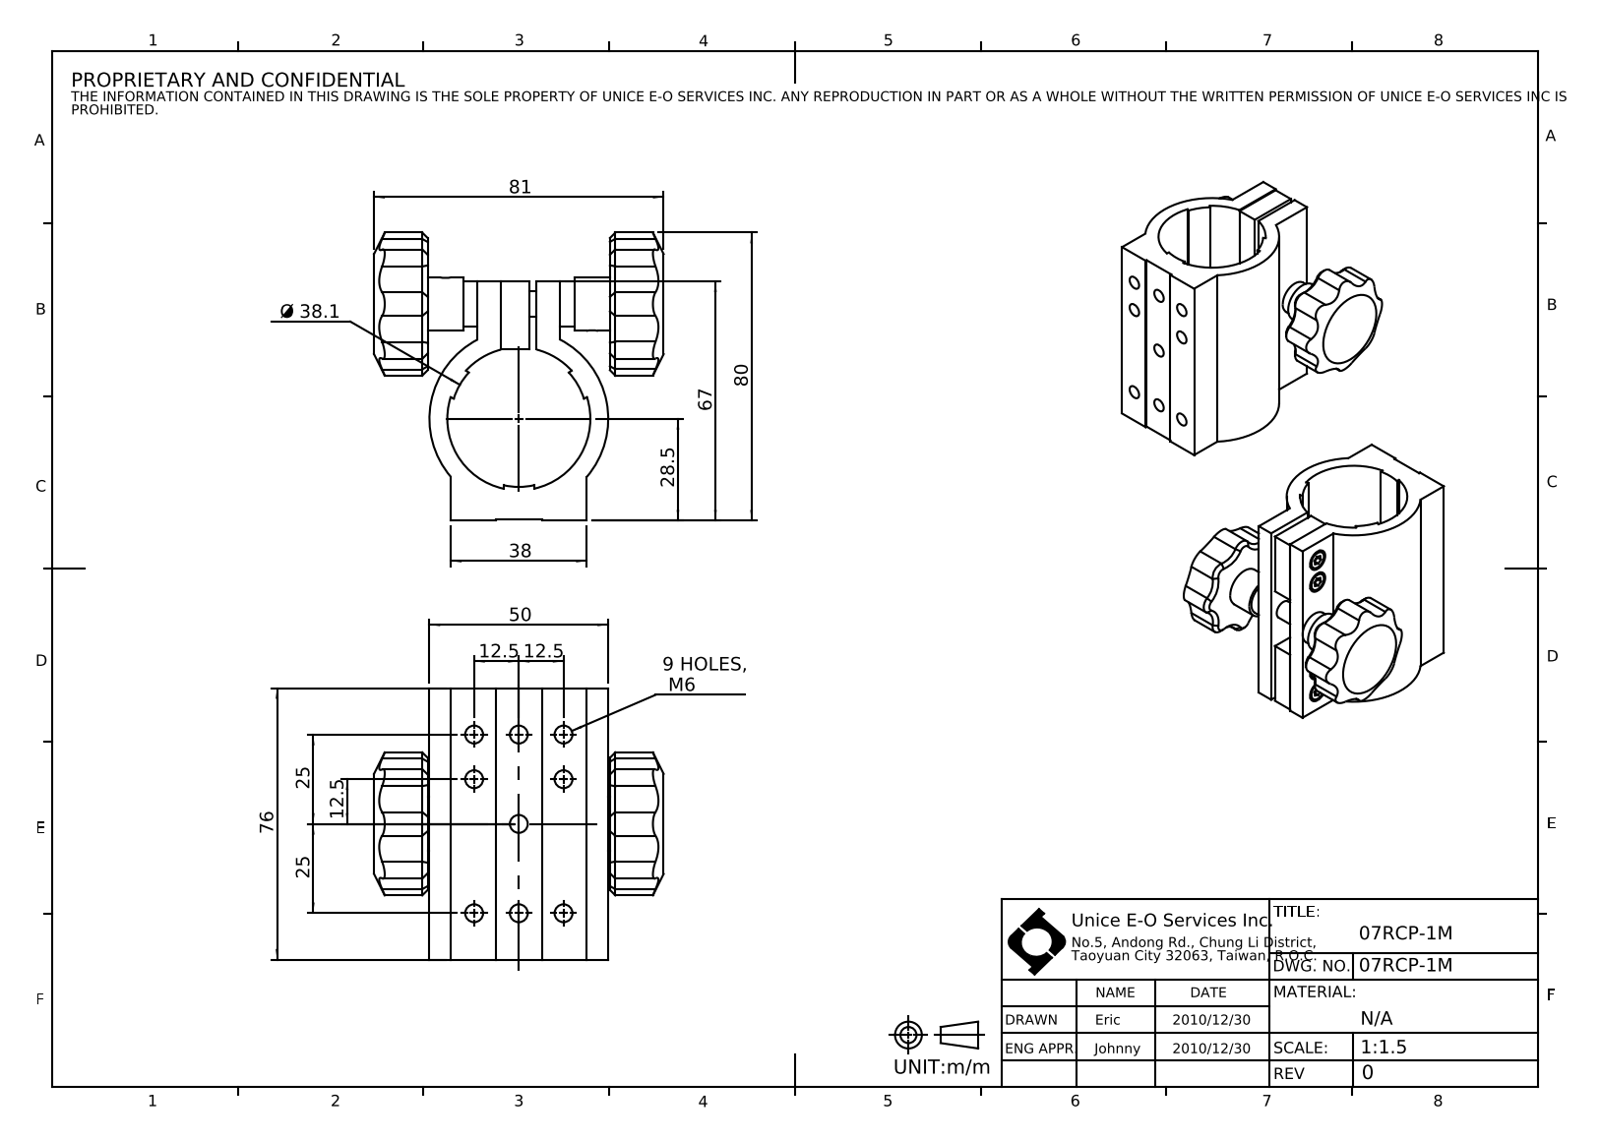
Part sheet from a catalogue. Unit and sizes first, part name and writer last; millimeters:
Units: millimetres
Overall size (bounding box): 81 × 80.6 × 76
Round holes (diameter × count): ⌀5 ×9, ⌀3.3 ×6, ⌀4.5 ×4, ⌀8 ×4, ⌀3 ×1, ⌀6.35 ×1, ⌀7 ×1, ⌀7.3 ×1
Round bosses / shafts (diameter × count): ⌀7 ×4, ⌀4 ×4, ⌀15 ×1, ⌀12.7 ×1, ⌀6 ×1
Partial cylindrical surfaces — rounded edges, fillets, slot ends (radius × count): R4 ×8, R7 ×8, R19.05 ×1, R20 ×1, R25 ×1
Main face-to-face distances: 6.5, 14, 30.5, 16.5, 10, 24, 20.5, 7.5, 37, 44.5
Hole centre spacings: 12.5, 27.95, 25, 50, 17.68, 26.25, 32.33, 41.4
Volume: 124 724 mm³ · Surface area: 46 537 mm²
Bodies: 12 solids, 353 faces (112 planar, 141 cylindrical, 100 other)
Part name (STEP PRODUCT): 07RCP-1M
STEP written by: SolidWorks 2016 (CONFIG_CONTROL_DESIGN)
